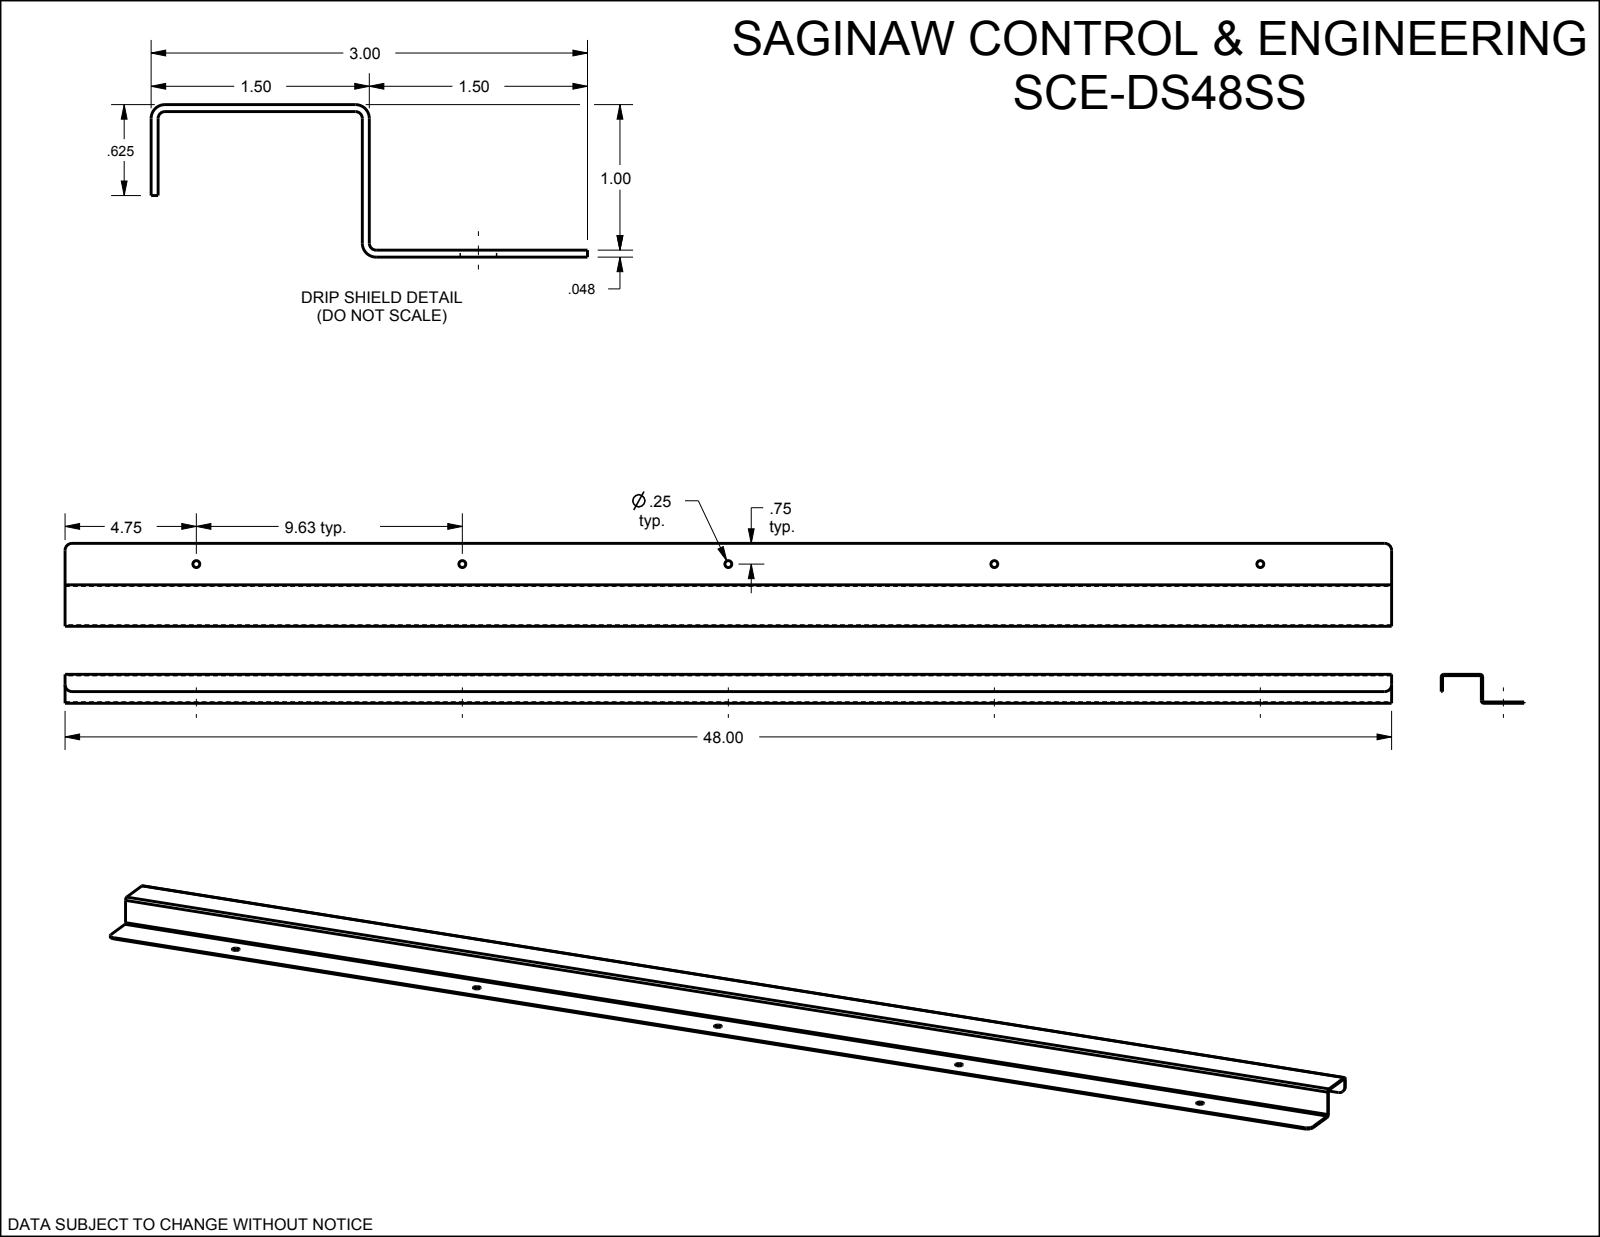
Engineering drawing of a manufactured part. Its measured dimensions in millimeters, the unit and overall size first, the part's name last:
Units: millimetres
Overall size (bounding box): 1219.2 × 76.2 × 26.6
Round holes (diameter × count): ⌀6.4 ×5
Partial cylindrical surfaces — rounded edges, fillets, slot ends (radius × count): R6.4 ×4, R1.2 ×3, R2.4 ×3
Main face-to-face distances: 1.2, 25.4, 24.2, 26.6, 36.9, 38.1, 35.7, 10.7, 9.5, 14.7
Hole centre spacings: 244.5, 244.5, 489, 733.4, 489, 977.9
Volume: 169 100 mm³ · Surface area: 280 800 mm²
Bodies: 1 solid, 27 faces (12 planar, 15 cylindrical, 0 other)
Part name (STEP PRODUCT): SCE-DS48SS
STEP written by: SolidWorks 2019 (CONFIG_CONTROL_DESIGN)
